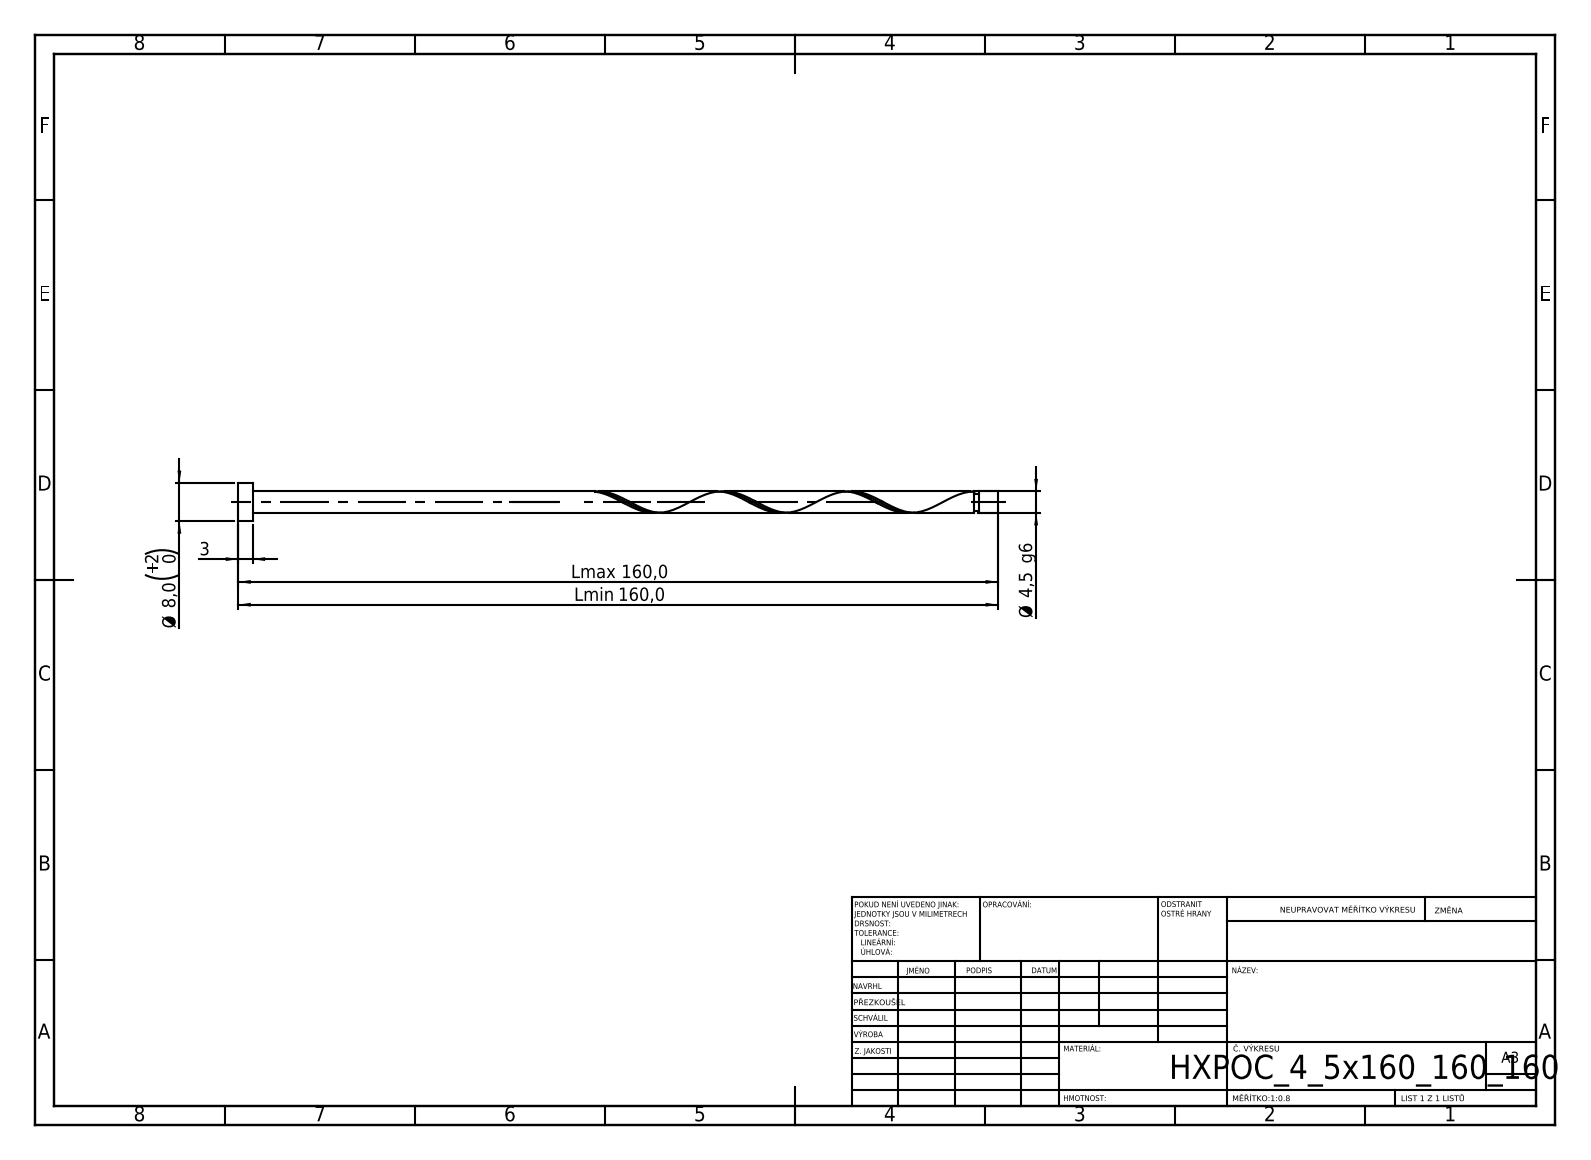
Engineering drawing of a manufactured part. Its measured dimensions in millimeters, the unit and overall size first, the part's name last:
Units: millimetres
Overall size (bounding box): 160 × 8 × 8
Round bosses / shafts (diameter × count): ⌀8 ×1, ⌀4.5 ×1, ⌀3.6 ×1
Main face-to-face distances: 3, 160, 157, 155.91, 152.91, 4.09, 155.01, 152.01, 0.9, 4.99
Volume: 2 618 mm³ · Surface area: 2 445 mm²
Bodies: 1 solid, 21 faces (6 planar, 14 cylindrical, 1 other)
STEP written by: SolidWorks 2019 (CONFIG_CONTROL_DESIGN)
